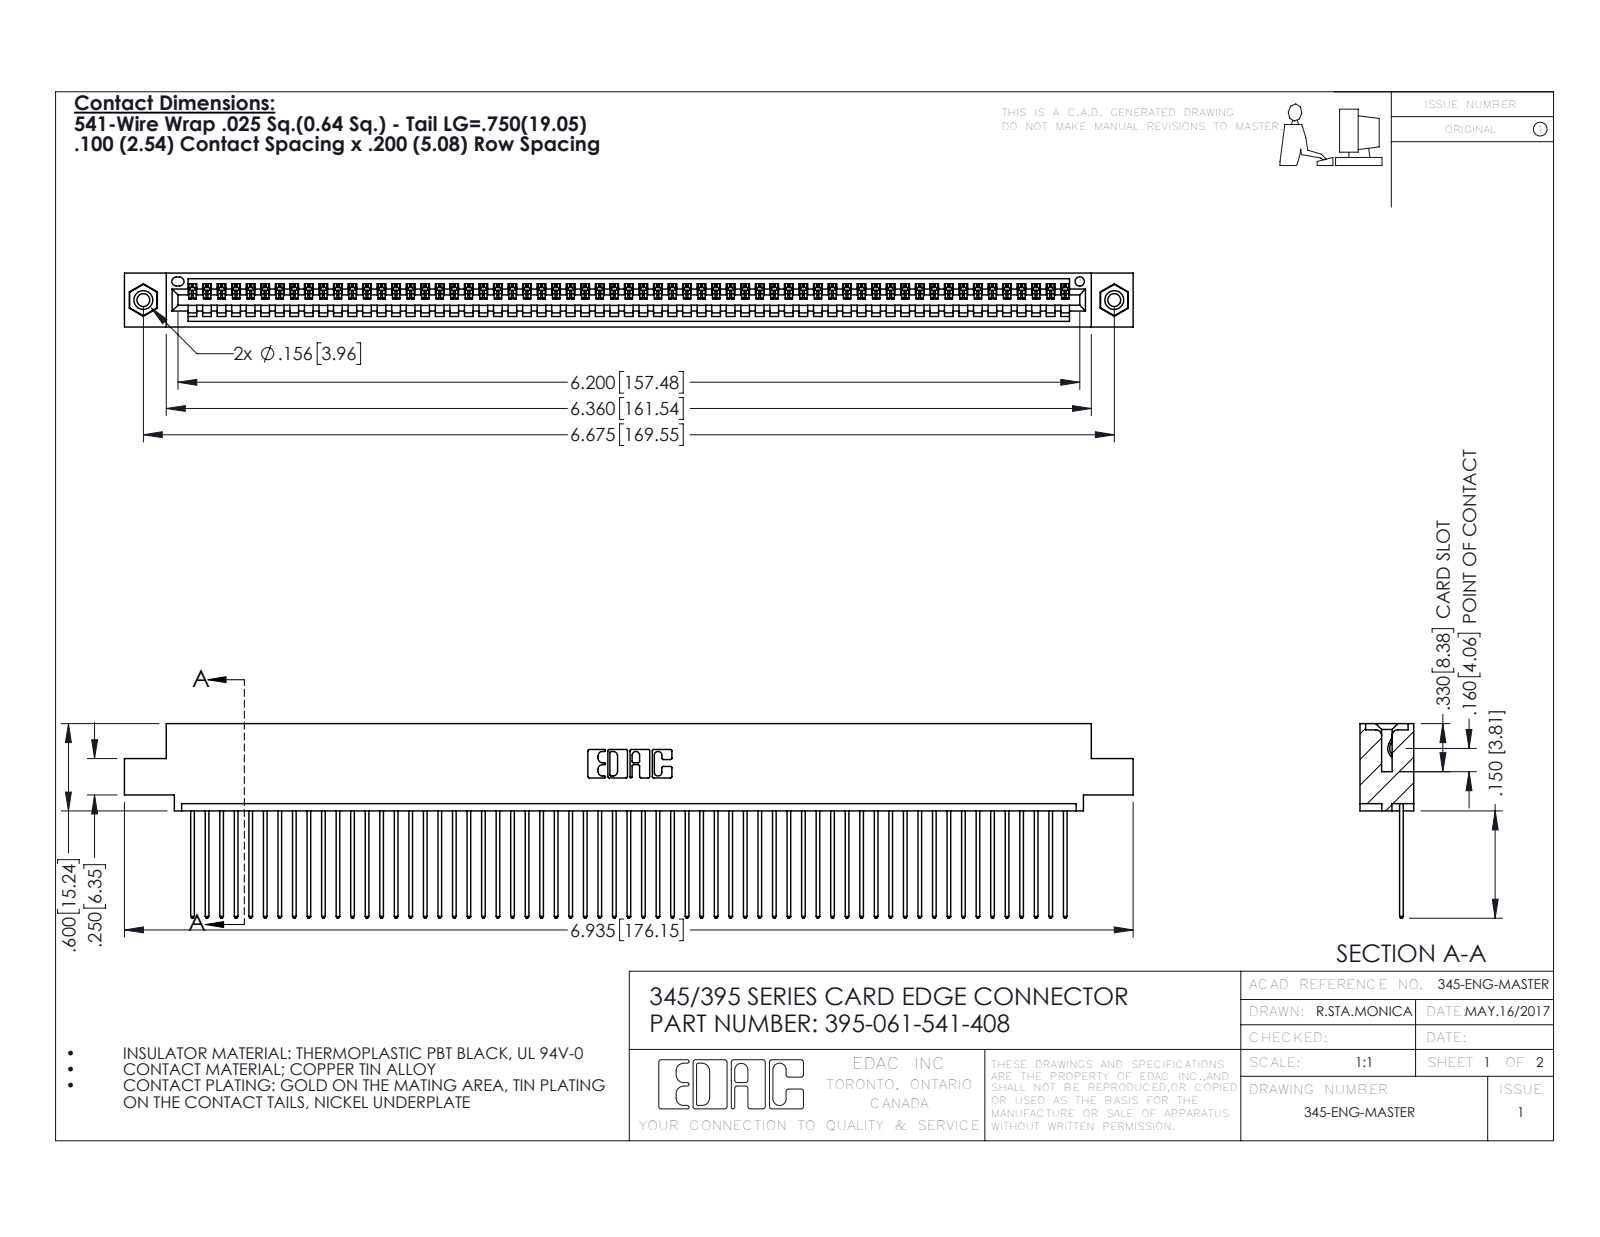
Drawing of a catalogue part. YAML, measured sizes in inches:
part_name: "345-250-001_345-250-003-102; 345-292-001_345-293-141; 345 Part_0.110 Offset - 0.156 Dia-TI; 395-061-541-408"
step_written_by: "SolidWorks 2016 (CONFIG_CONTROL_DESIGN)"
units: inches
bodies: {solids: 64, faces: 3728, planar: 2556, cylindrical: 1156, other: 16}
overall_size: [6.935, 1.337, 0.37]
volume: 1.038
surface_area: 37.43
round_holes:
  - {diameter: 0.089, count: 2}
  - {diameter: 0.125, count: 2}
  - {diameter: 0.156, count: 2}
  - {diameter: 0.064, count: 1}
round_bosses_or_shafts:
  - {diameter: 0.155, count: 2}
partial_cylinders:
  - {radius: 0.006, count: 122}
  - {radius: 0.01, count: 122}
  - {radius: 0.01, count: 22}
  - {radius: 0.007, count: 6}
  - {radius: 0.031, count: 6}
  - {radius: 0.026, count: 3}
  - {radius: 0.031, count: 2}
  - {radius: 0.04, count: 2}
face_to_face_distances: [0.072, 0.298, 0.098, 0.272, 0.025, 0.37, 0.2, 0.225, 0.149, 0.072]
hole_center_spacings: [0.27, 6.439, 6.675]
